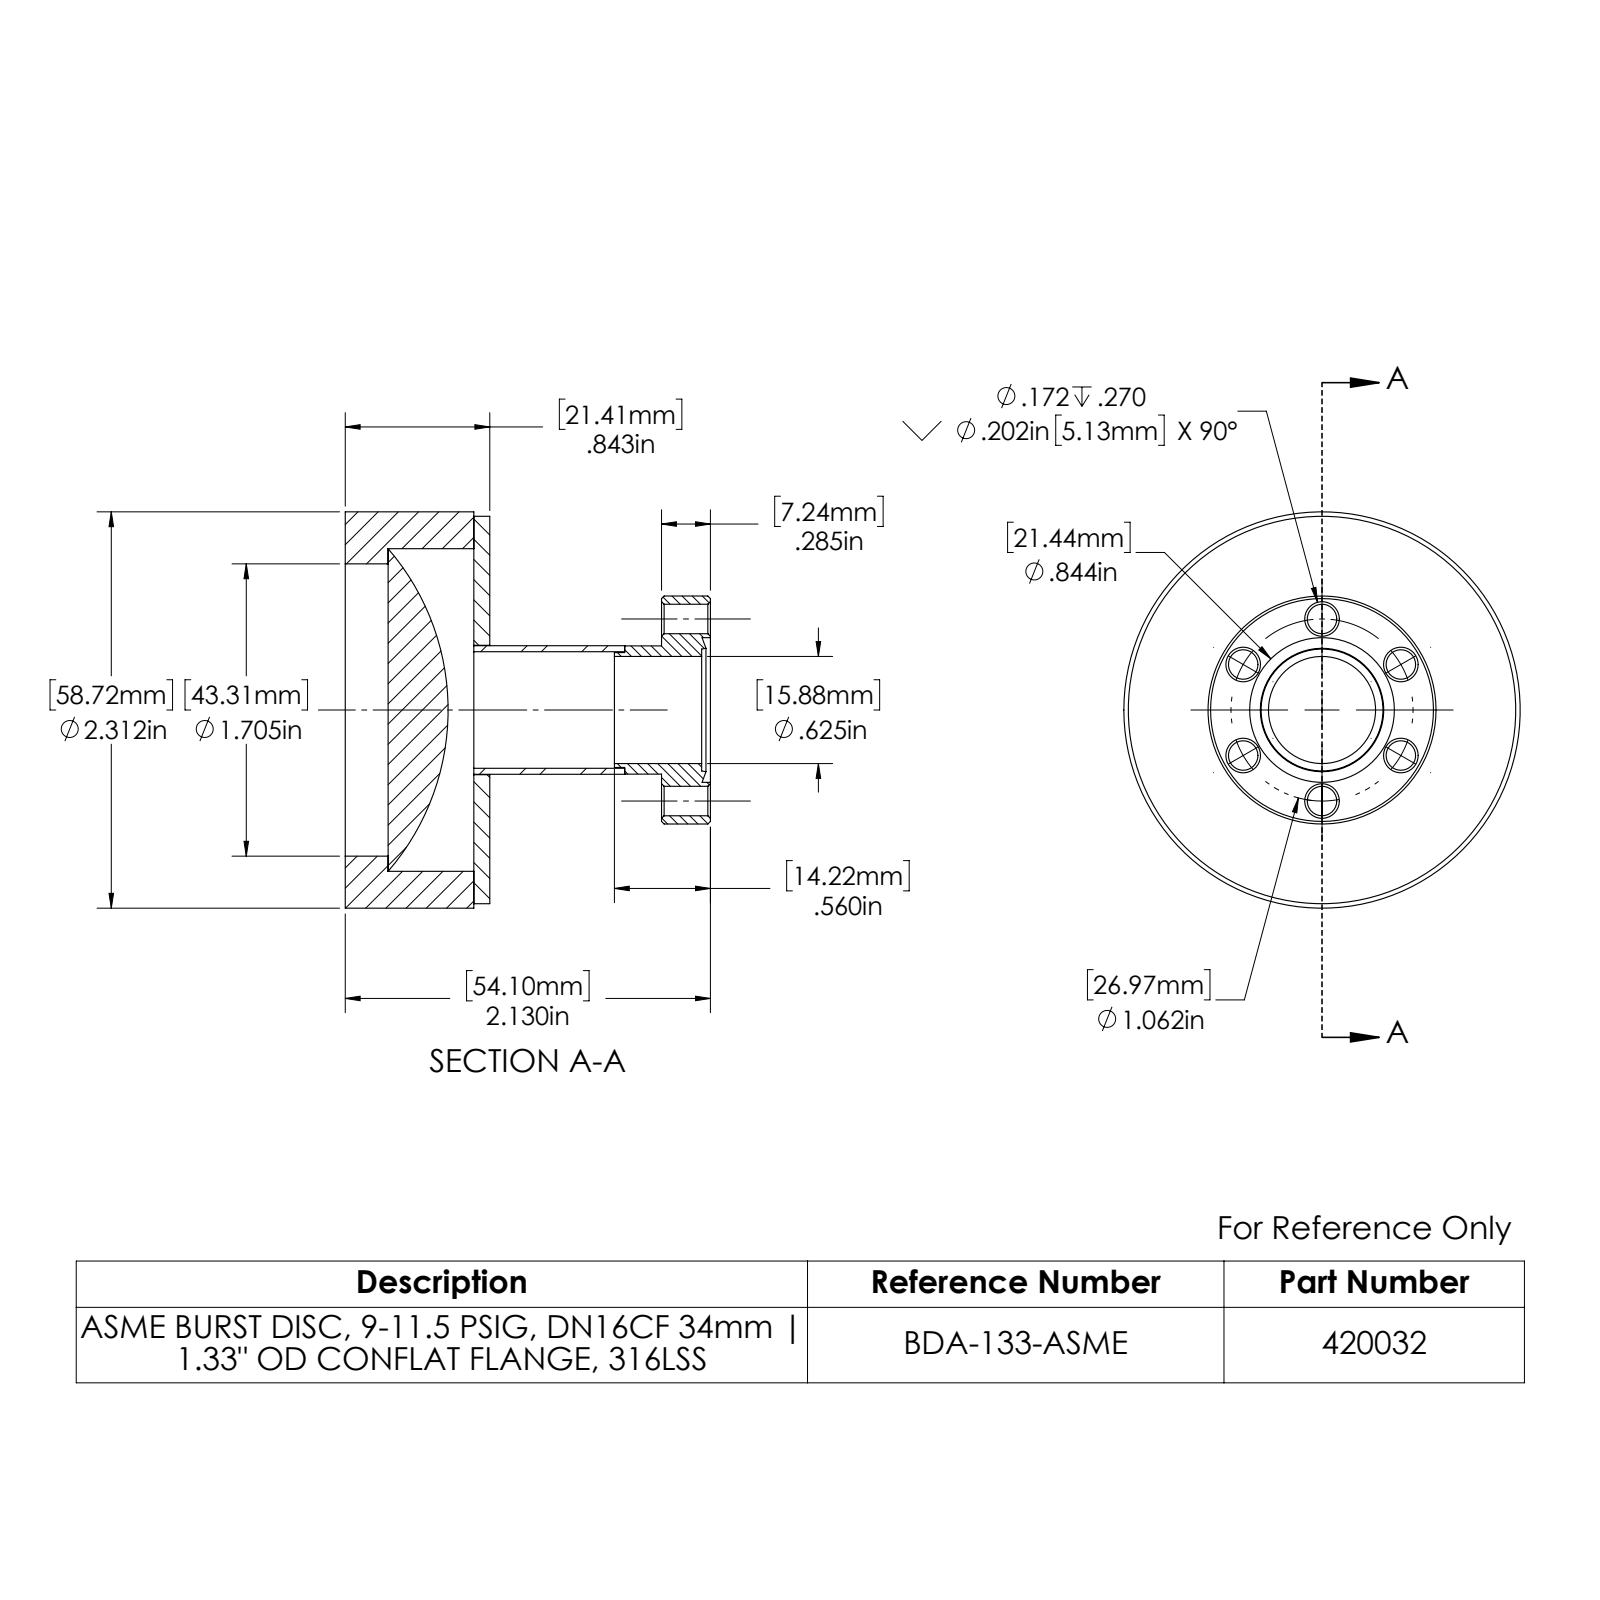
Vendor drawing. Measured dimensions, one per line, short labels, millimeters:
name: 420032; 942002; 110004; 942004 (+1 more)
written by: SolidWorks 2022 (AUTOMOTIVE_DESIGN)
unit: mm
bodies: 5 solids, 83 faces (13 planar, 36 cylindrical, 34 other)
size: 58.7 × 58.7 × 54.1
volume: 39 070 mm³; area: 24 080 mm²
holes: 6× ⌀4.4, 1× ⌀15.9, 1× ⌀17.3, 1× ⌀19.2, 1× ⌀21.4, 1× ⌀43.3, 1× ⌀47.8
bosses: 1× ⌀58.7, 1× ⌀57.4, 1× ⌀33.8, 1× ⌀19.1, 1× ⌀19, 1× ⌀17
face distances: 2.4, 12.7, 15.1, 6.4, 19.1, 21.4, 35.1, 46.9, 40.5, 27.8
hole spacings: 13.5, 23.4, 27, 23.4
